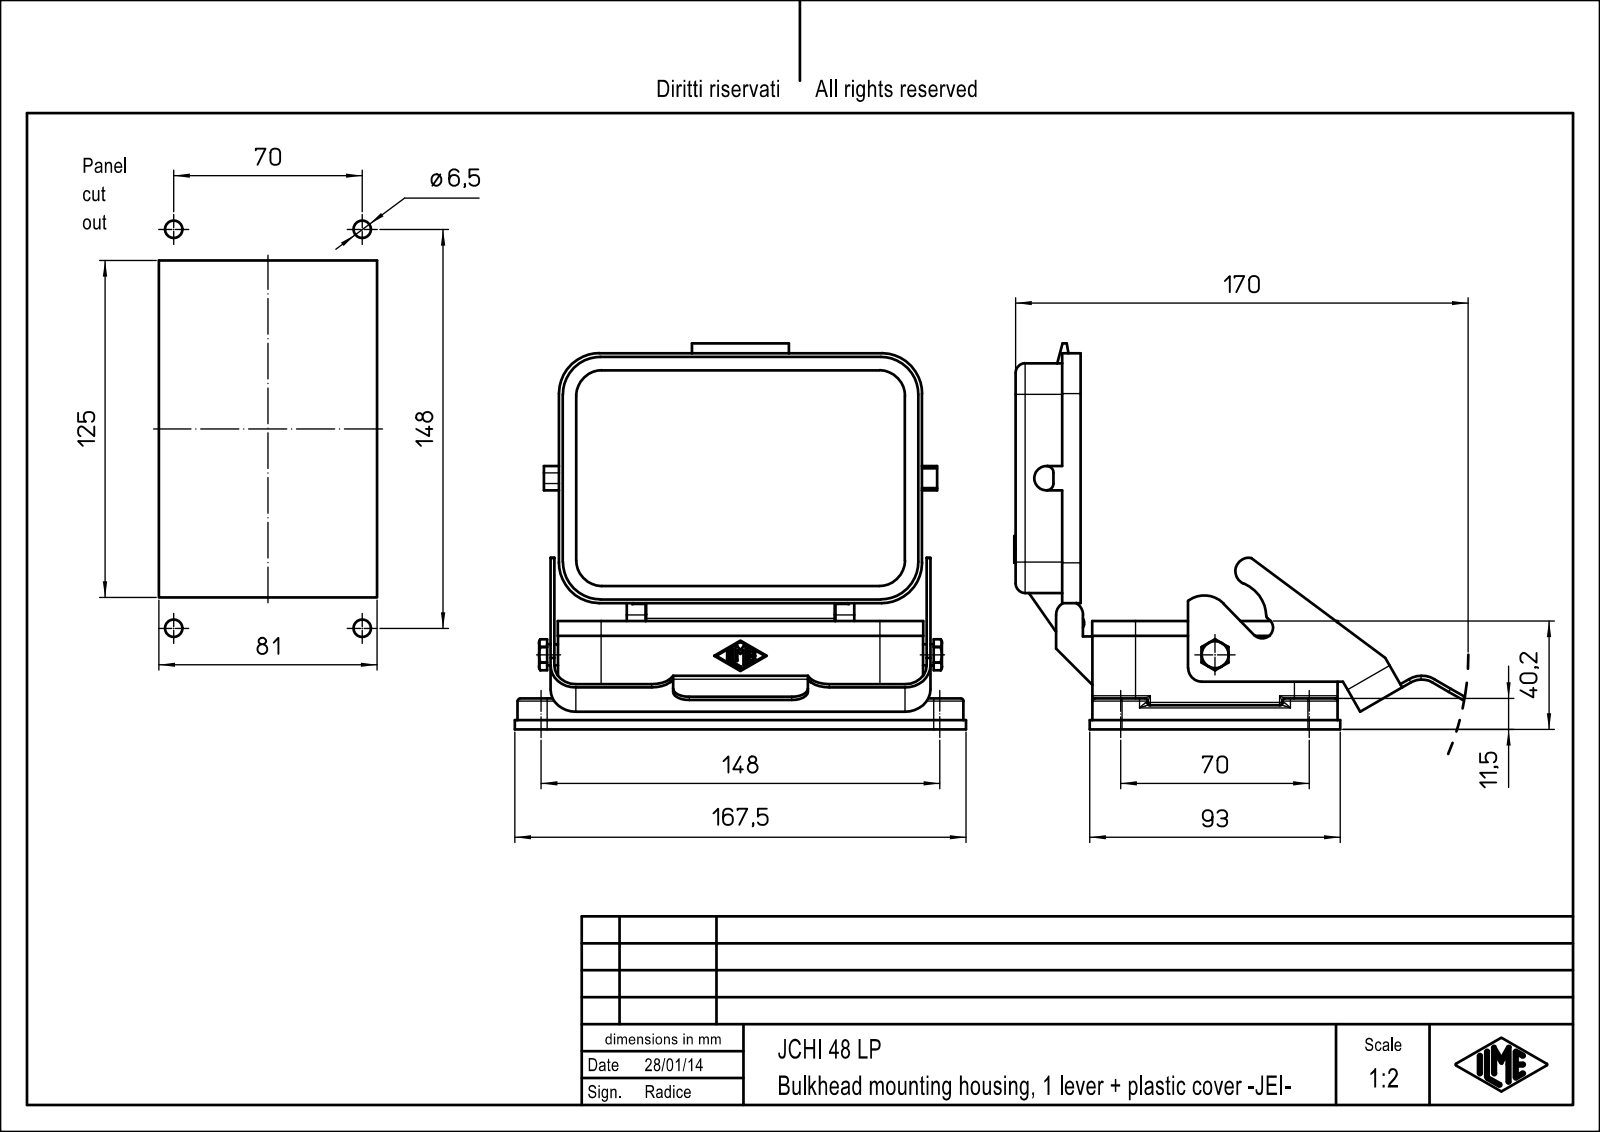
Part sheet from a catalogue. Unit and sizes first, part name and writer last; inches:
Units: inches
Overall size (bounding box): 6.594 × 6.583 × 5.638
Round holes (diameter × count): ⌀0.097 ×8, ⌀0.122 ×8, ⌀0.256 ×4, ⌀0.26 ×4, ⌀0.472 ×4
Round bosses / shafts (diameter × count): ⌀0.307 ×1, ⌀0.236 ×1, ⌀0.197 ×1
Partial cylindrical surfaces — rounded edges, fillets, slot ends (radius × count): R0.039 ×35, R0.013 ×15, R0.015 ×14, R0.118 ×13, R0.433 ×8, R0.315 ×5, R0.394 ×5, R0.138 ×4
Main face-to-face distances: 0.197, 0.118, 3.386, 0.055, 5.496, 0.201, 4.587, 4.705, 5.138, 0.305
Hole centre spacings: 0.88, 1.063, 1.378, 1.496, 1.763, 2.739, 4.094, 4.23
Volume: 12.47 in³ · Surface area: 177.2 in²
Bodies: 1 solid, 624 faces (299 planar, 267 cylindrical, 58 other)
Part name (STEP PRODUCT): JCHI_48_LP
STEP written by: Creo Elements/Direct Modeling 18.0B 02-Dec-2011 (C) Parametric Technology GmbH (AUTOMOTIVE_DESIGN)
